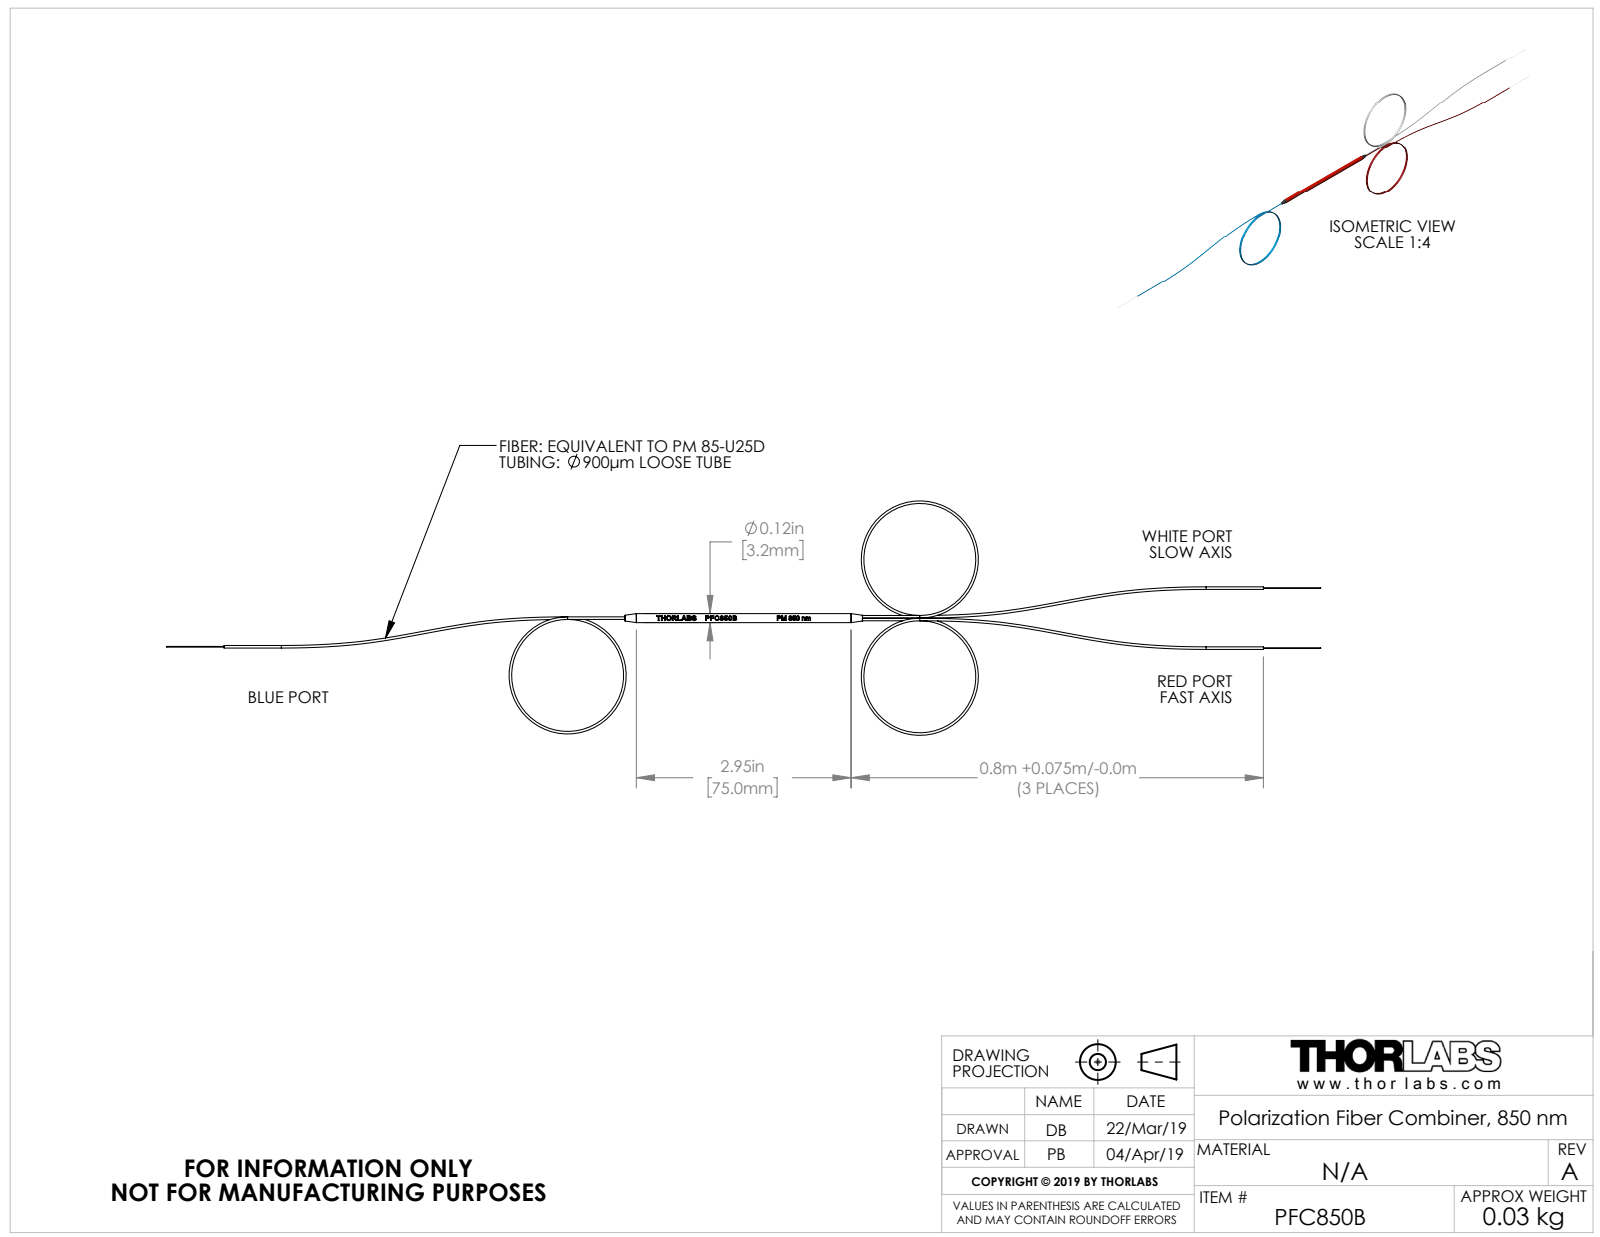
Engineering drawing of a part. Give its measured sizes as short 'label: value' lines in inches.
name: DWG1751_42-2mm; PANDA 850_60; DWG1631_75mm; DWG1528 (+8 more)
written by: SolidWorks 2018 (CONFIG_CONTROL_DESIGN)
unit: in
bodies: 14 solids, 255 faces (41 planar, 154 cylindrical, 60 other)
size: 15.866 × 3.222 × 0.193
volume: 0.051 in³; area: 11.44 in²
holes: 6× ⌀0.02, 3× ⌀0.037, 1× ⌀0.106
bosses: 6× ⌀0.035, 5× ⌀0.01, 1× ⌀0.124, 1× ⌀0.098
rounds: 2× R0.018, 1× R0.039
face distances: 0.118, 2.717, 2.835, 0.236, 2.598, 2.953, 2.48, 2.303, 2.067, 0.65
hole spacings: 0.402, 0.42, 0.438, 0.019, 0.019, 0.037, 0.159, 0.383
